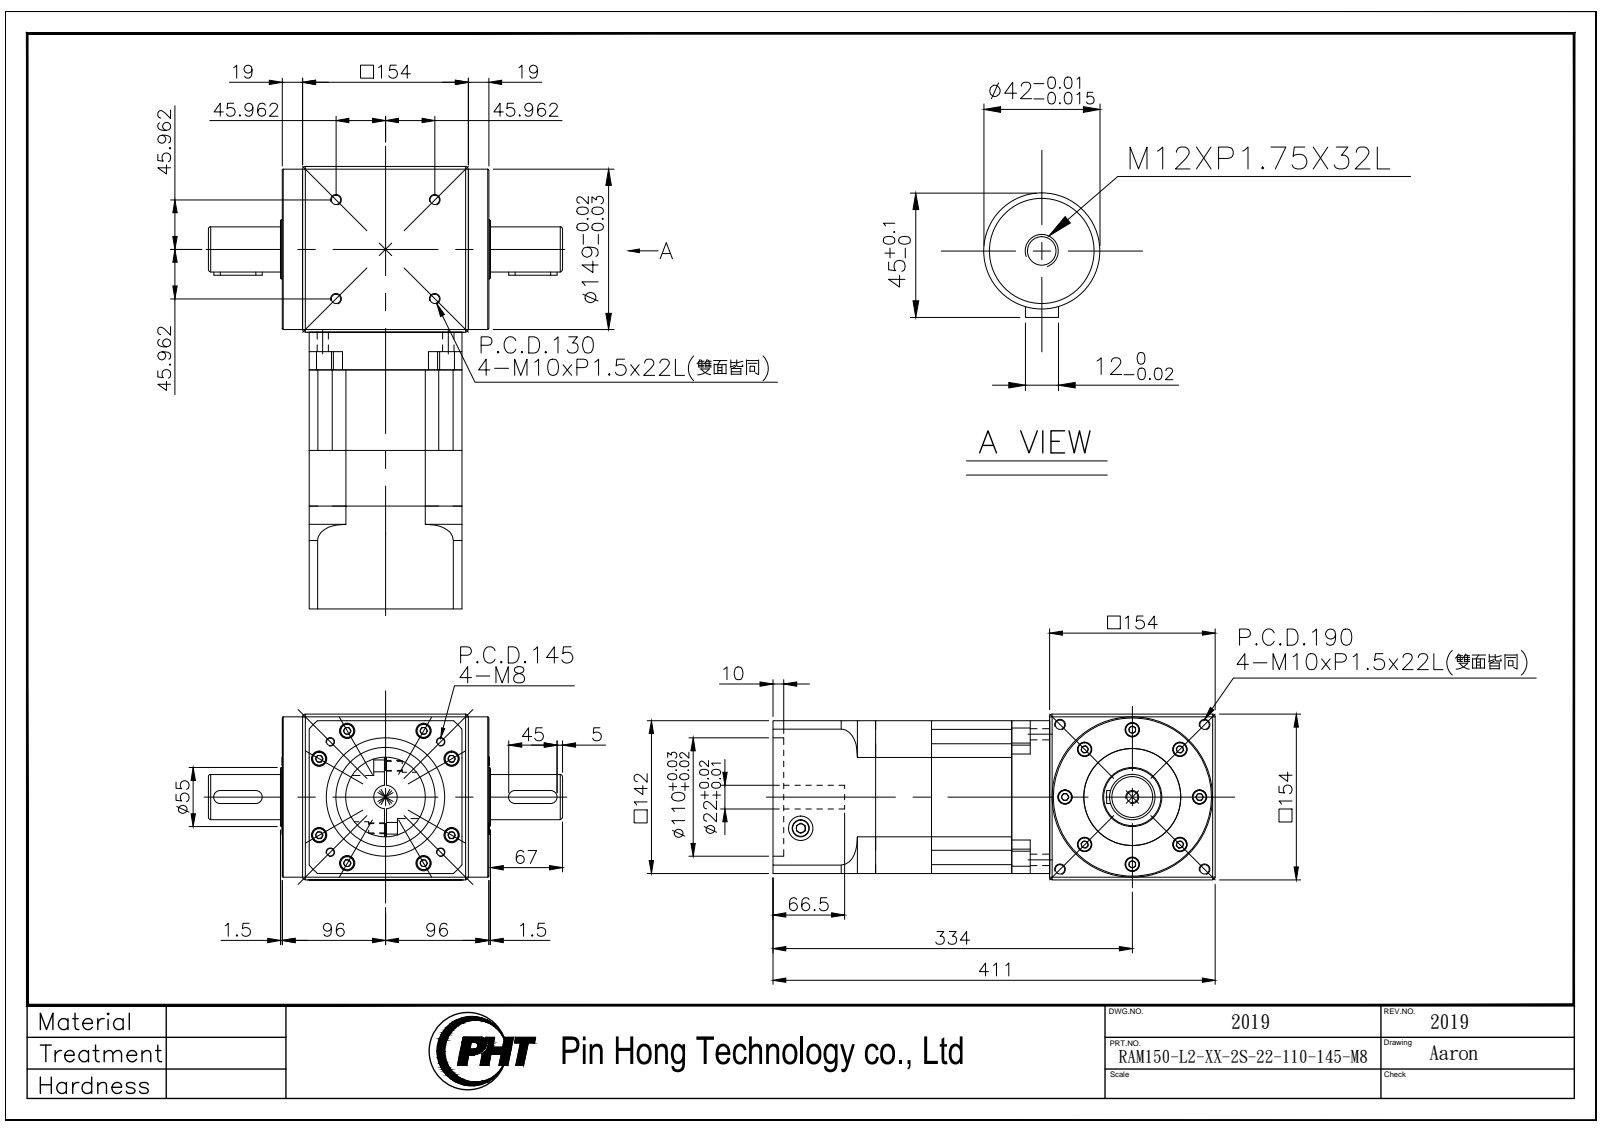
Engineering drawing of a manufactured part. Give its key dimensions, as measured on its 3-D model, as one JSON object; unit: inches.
{"part_name": "RAM150-L2-XX-2S-22-110-145-M8_2019", "step_written_by": "SolidWorks 2016 (AUTOMOTIVE_DESIGN)", "units": "inches", "bodies": {"solids": 7, "faces": 909, "planar": 441, "cylindrical": 304, "other": 164}, "overall_size": [16.181, 12.953, 6.063], "volume_in3": 546.9, "surface_area_in2": 915.7, "round_holes": [[0.335, 12], [0.354, 8], [0.433, 8], [0.551, 8], [0.689, 8], [0.268, 4], [0.413, 4], [0.886, 2], [0.161, 1], [0.402, 1], [0.866, 1], [3.622, 1]], "round_bosses_or_shafts": [[0.63, 12], [0.512, 8], [5.866, 1], [5.118, 1], [3.543, 1], [2.913, 1], [2.165, 1], [1.654, 1]], "partial_cylinders_radius": [[0.236, 4], [0.394, 4], [3.15, 1], [3.74, 1], [4.228, 1]], "face_to_face_distances": [0.236, 5.827, 6.063, 5.591, 2.039, 4.98, 2.941, 1.378, 6.358, 4.319], "hole_center_spacings": [2.795, 0.737, 0.74, 0.908, 1.883, 2.651, 3.265, 3.44]}
